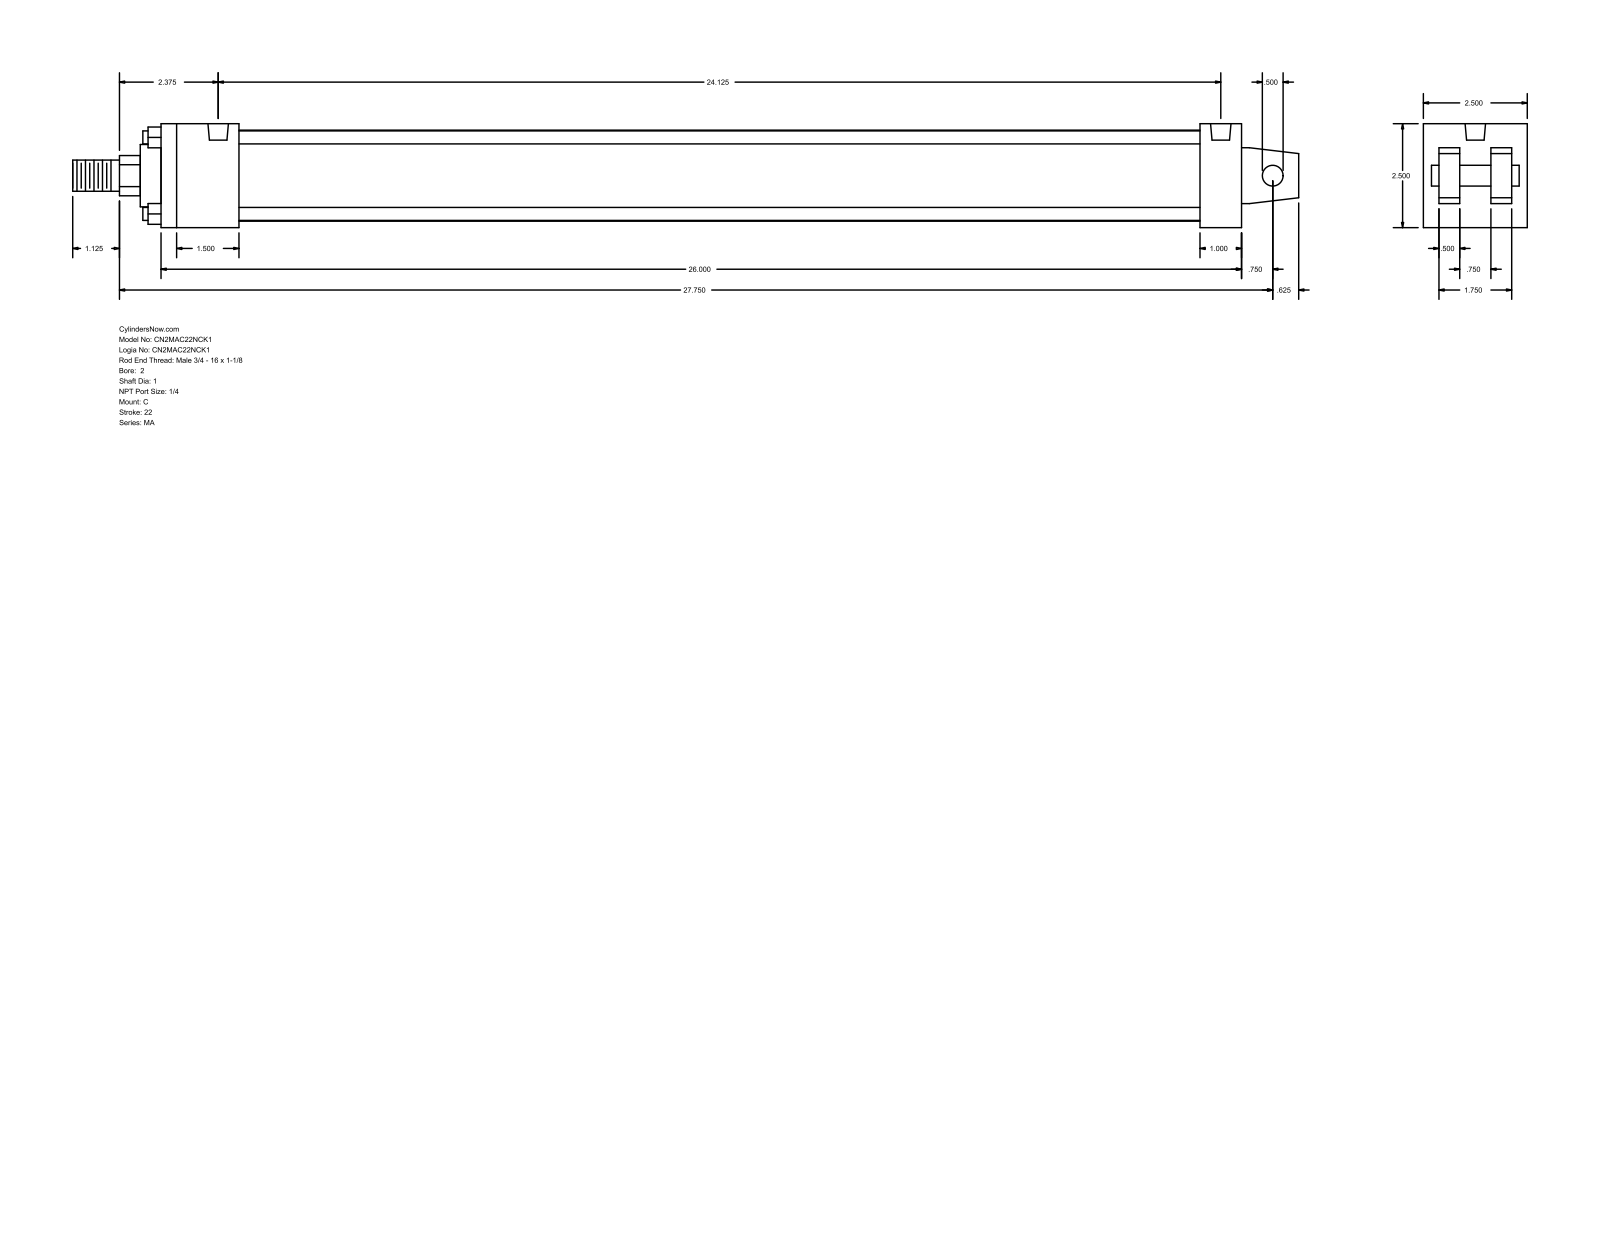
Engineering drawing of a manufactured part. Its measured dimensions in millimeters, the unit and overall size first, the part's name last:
Units: millimetres
Overall size (bounding box): 749.3 × 63.5 × 63.5
Round holes (diameter × count): ⌀7.94 ×4, ⌀12.49 ×2
Round bosses / shafts (diameter × count): ⌀7.94 ×4, ⌀55.63 ×1, ⌀38.1 ×1, ⌀25.4 ×1, ⌀19.05 ×1, ⌀12.7 ×1
Partial cylindrical surfaces — rounded edges, fillets, slot ends (radius × count): R12.29 ×1
Main face-to-face distances: 63.5, 12.7, 660.4, 22.22, 41.28, 9.52, 53.98, 31.76, 47.63, 25.4
Hole centre spacings: 612.77
Bodies: 0 solids, 103 faces (76 planar, 27 cylindrical, 0 other)
Part name (STEP PRODUCT): MA_C__0200_1
STEP written by: GSSL Pune (CONFIG_CONTROL_DESIGN)
